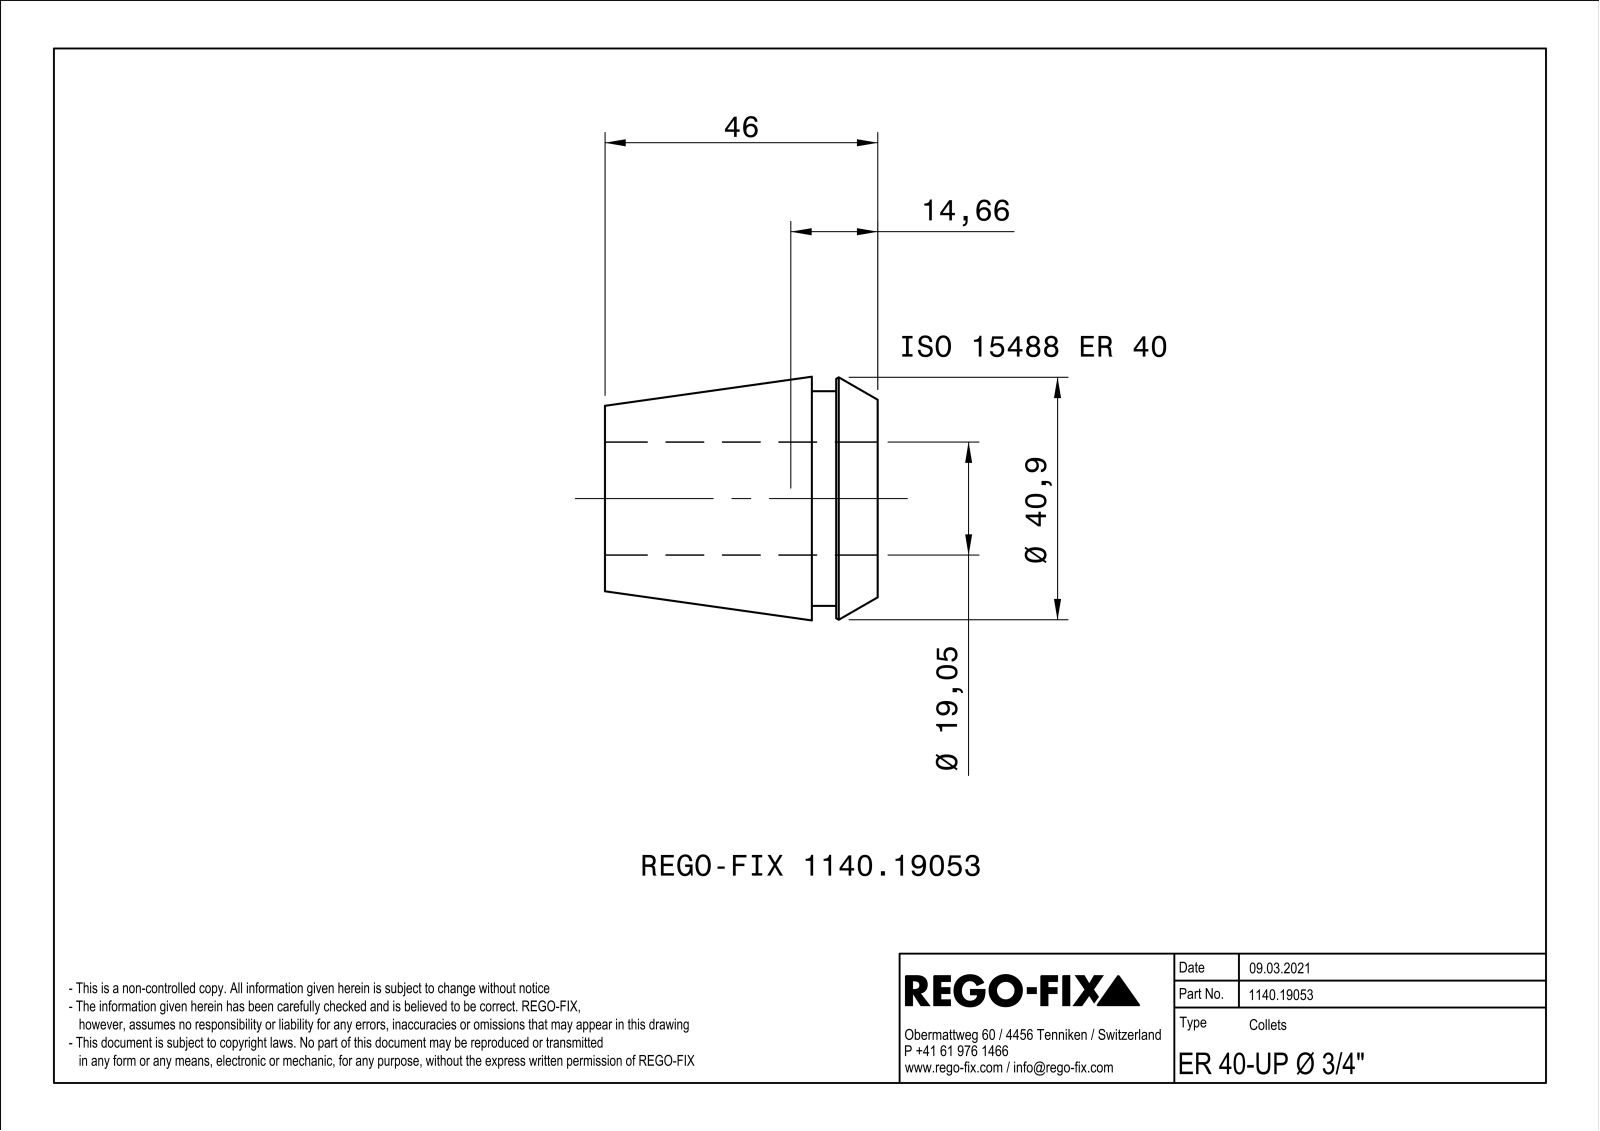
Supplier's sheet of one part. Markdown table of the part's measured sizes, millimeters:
| quantity | value |
| --- | --- |
| part name | NOCUT |
| STEP written by | SIEMENS PLM Software Solid Edge ST10 (AUTOMOTIVE_DESIGN) |
| units | millimeters |
| bodies | 1 solid, 177 faces (88 planar, 9 cylindrical, 80 other) |
| overall size | 46 × 40.99 × 40.99 |
| volume | 29 100 mm³ |
| surface area | 19 622 mm² |
| round holes (diameter × count) | 19.05 × 1 |
| round bosses / shafts (diameter × count) | 36.2 × 1 |
| main face-to-face distances | 1, 46, 11.1, 34.9, 7, 4.1, 39, 7.5, 0.5, 3.6 |
